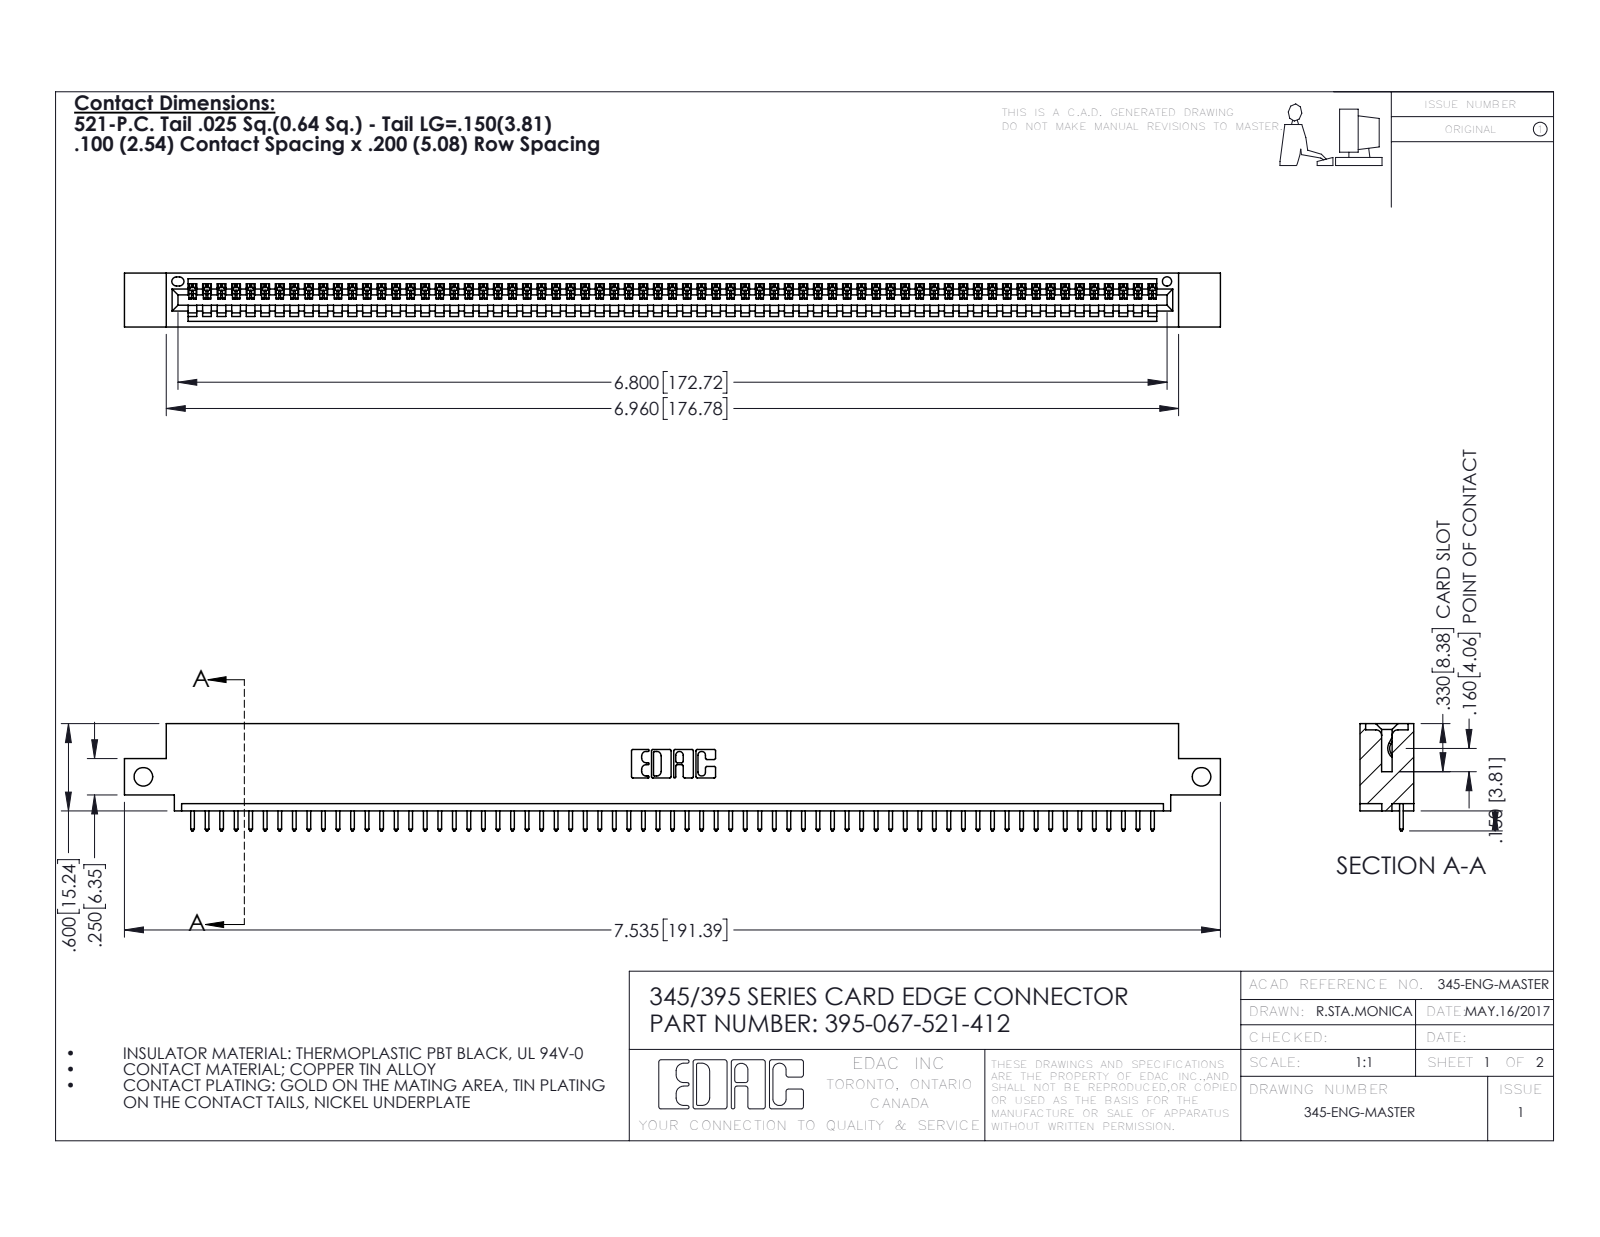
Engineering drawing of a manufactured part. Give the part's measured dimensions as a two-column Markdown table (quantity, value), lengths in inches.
| quantity | value |
| --- | --- |
| part name | 395-067-521-412; 345 Part_0.110 Offset - Side Mount; 345-292-001_345-293-121 |
| STEP written by | SolidWorks 2016 (CONFIG_CONTROL_DESIGN) |
| units | inches |
| bodies | 68 solids, 4016 faces (2764 planar, 1252 cylindrical, 0 other) |
| overall size | 7.535 × 0.737 × 0.37 |
| volume | 1.1 in³ |
| surface area | 36.42 in² |
| round holes (diameter × count) | 0.128 × 2, 0.064 × 1 |
| partial cylindrical surfaces (radius × count) | 0.006 × 134, 0.01 × 134, 0.01 × 22, 0.007 × 6, 0.031 × 6, 0.026 × 3, 0.031 × 2, 0.04 × 2 |
| main face-to-face distances | 0.298, 0.072, 0.37, 0.2, 0.098, 0.272, 0.025, 0.225, 0.149, 0.072 |
| hole center spacings | 7.275 |
